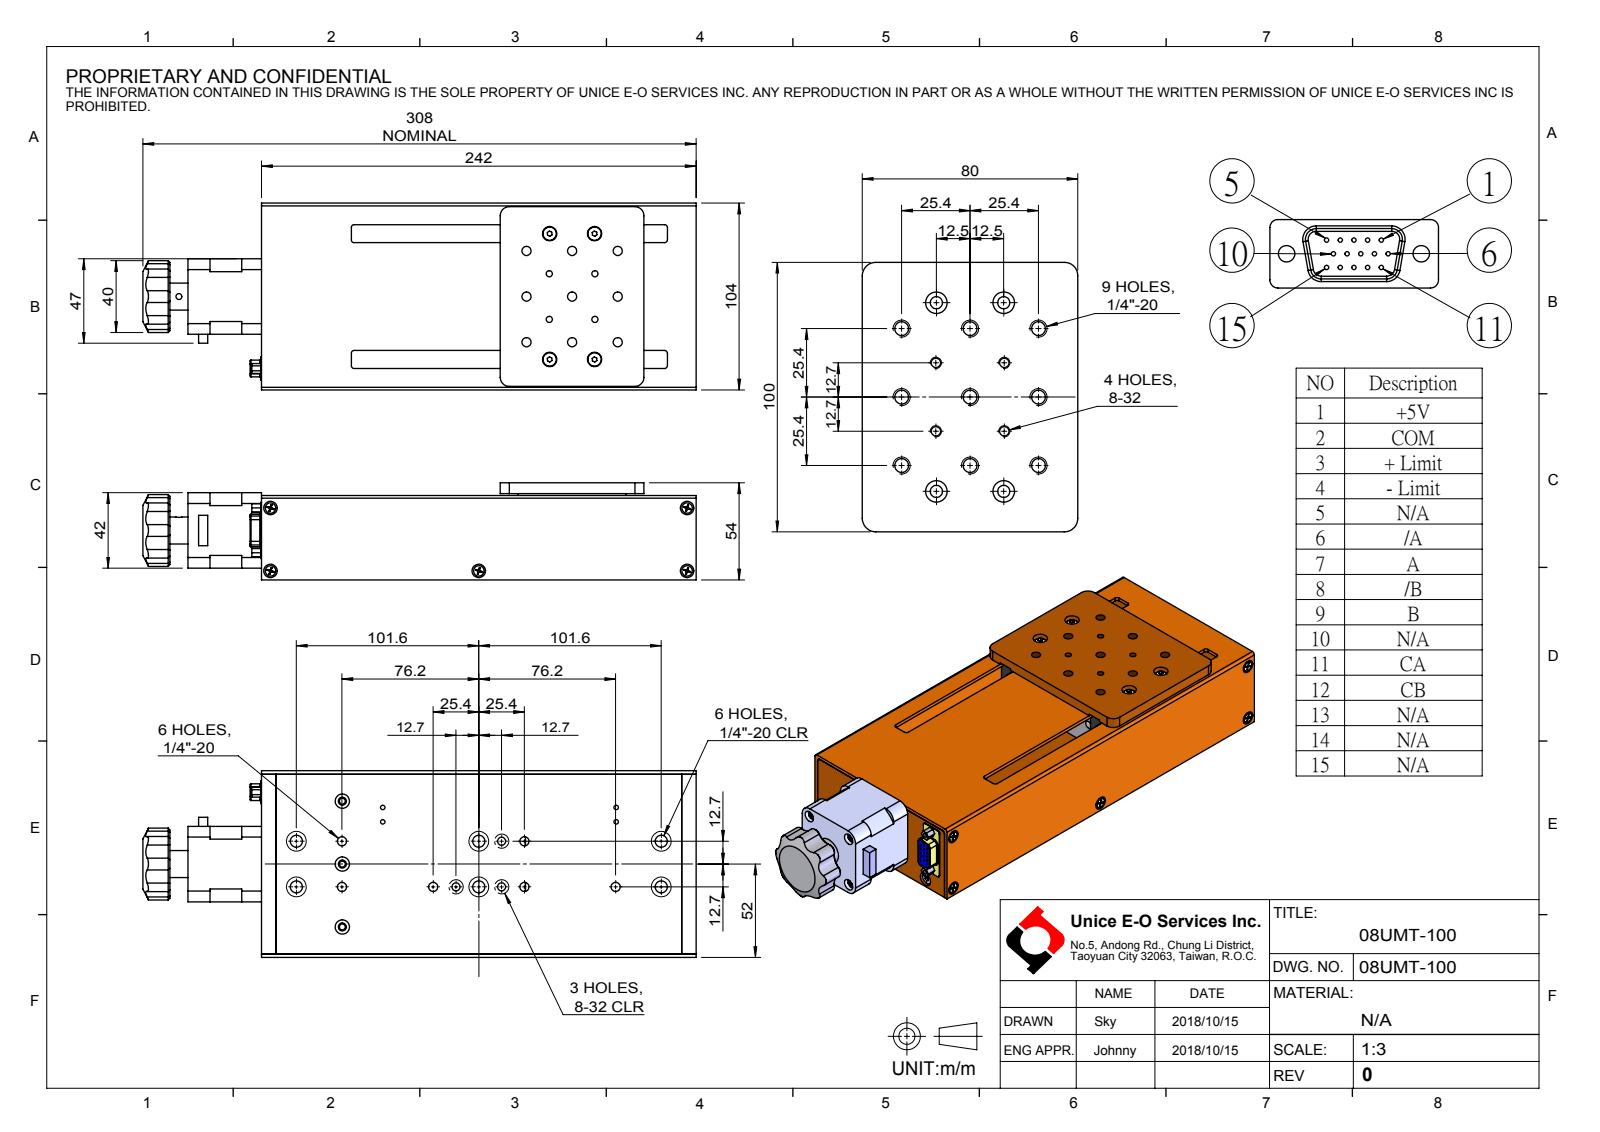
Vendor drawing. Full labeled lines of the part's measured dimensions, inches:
Part name (STEP PRODUCT): 08UMT-100
STEP written by: SolidWorks 2016 (AUTOMOTIVE_DESIGN)
Units: inches
Bodies: 0 solids, 679 faces (279 planar, 260 cylindrical, 140 other)
Overall size (bounding box): 12.126 × 4.094 × 2.126
Round holes (diameter × count): ⌀0.031 ×15, ⌀0.201 ×15, ⌀0.315 ×10, ⌀0.098 ×6, ⌀0.266 ×6, ⌀0.437 ×6, ⌀0.136 ×4, ⌀0.256 ×4, ⌀0.177 ×3, ⌀0.177 ×2, ⌀0.591 ×1, ⌀0.827 ×1
Round bosses / shafts (diameter × count): ⌀0.228 ×5
Partial cylindrical surfaces — rounded edges, fillets, slot ends (radius × count): R0.02 ×21, R0.059 ×15, R0.157 ×8, R0.292 ×8, R0.079 ×6, R0.118 ×4, R0.197 ×4, R0.236 ×4
Main face-to-face distances: 0.079, 4.016, 0.394, 1.85, 1.772, 1.378, 1.457, 4.094, 3.937, 0.276
Hole centre spacings: 1, 0.112, 0.18, 0.2, 0.1, 0.269, 1.414, 0.224
